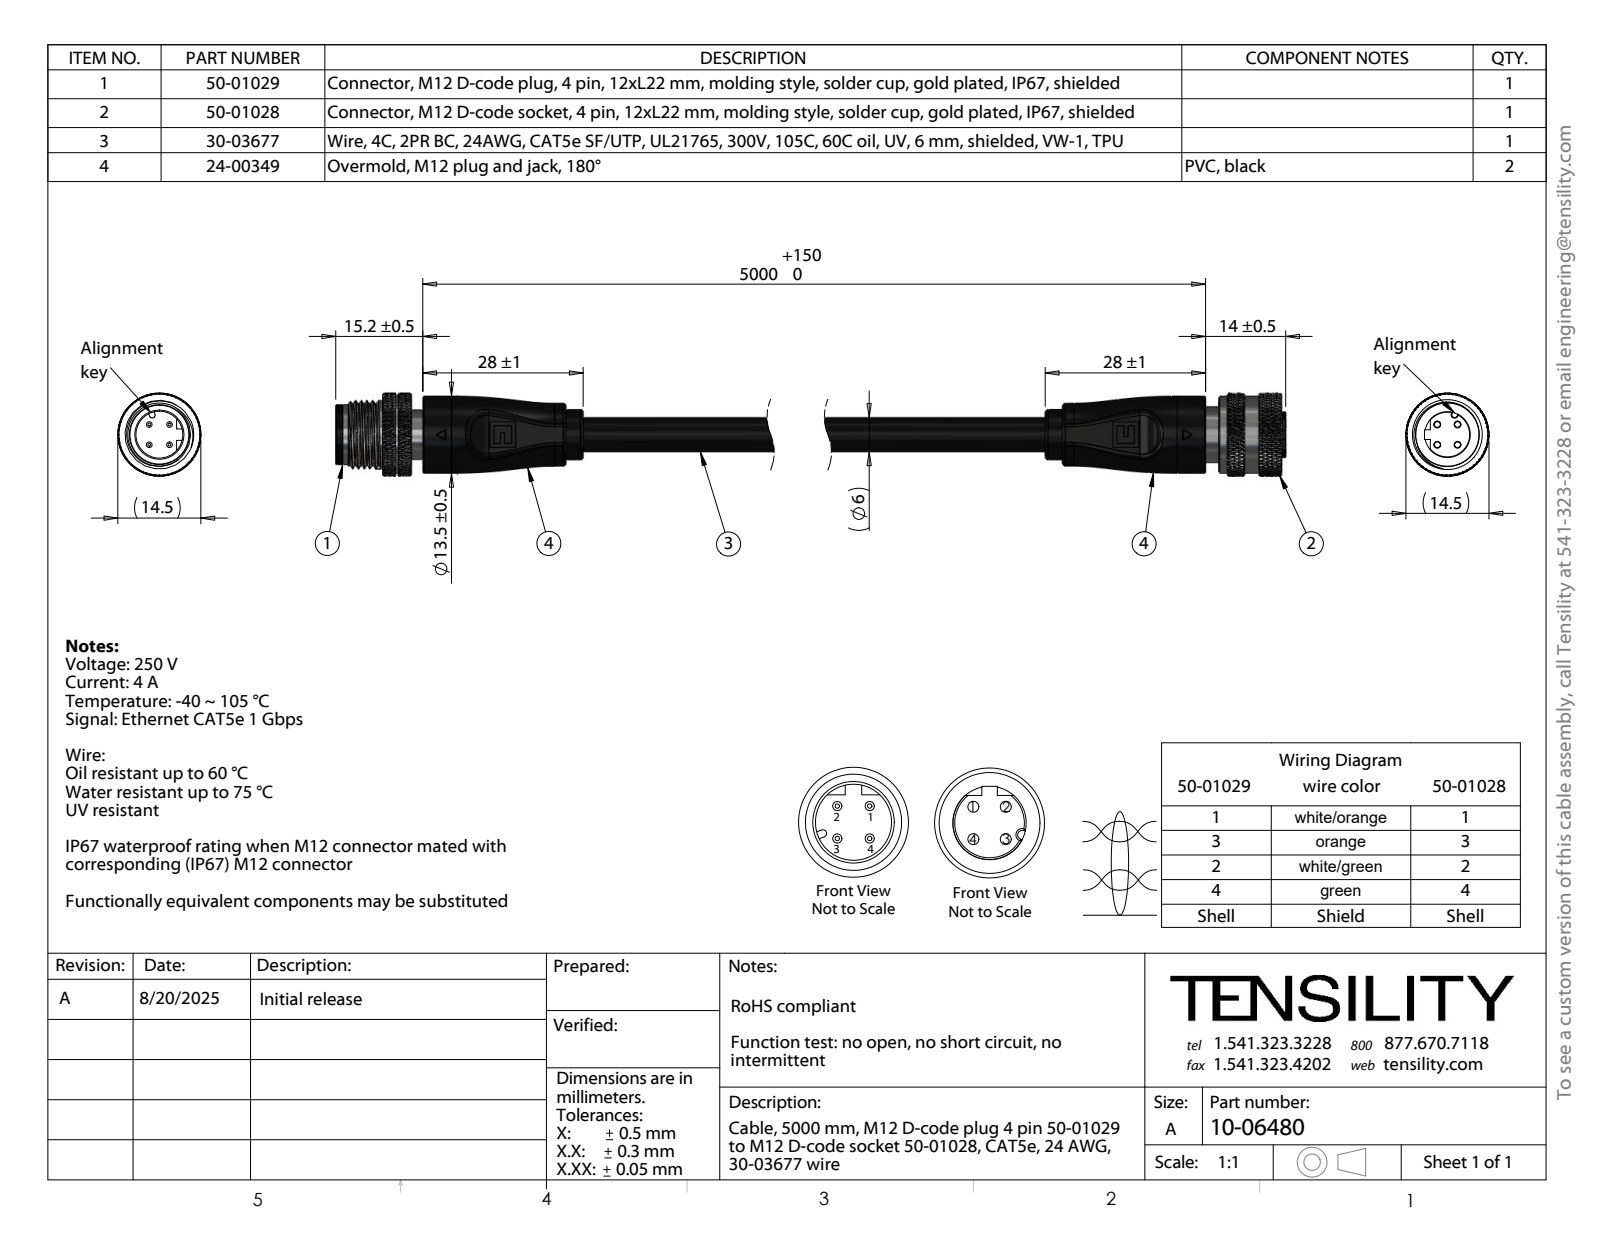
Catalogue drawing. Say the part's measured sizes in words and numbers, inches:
The part is named "24-00349_Mexico; 50-01028-03_默认; 50-01029-01_默认; 50-01029_默认 (+8 more)". Its 3-D file was written by "SolidWorks 2025 (CONFIG_CONTROL_DESIGN)". It is 53 solids with 5792 faces: 362 planar, 1477 cylindrical and 3953 other. Overall it measures 9.26 by 0.571 by 0.571 inches. Its volume is 0.838 cubic inches and its surface area 47.49 square inches. Round holes: 28 of diameter 0.008, 4 of diameter 0.039, 4 of diameter 0.041, 4 of diameter 0.043, 4 of diameter 0.047, 1 of diameter 0.124, 1 of diameter 0.126, 1 of diameter 0.14, 1 of diameter 0.323, 1 of diameter 0.374, 1 of diameter 0.394, 1 of diameter 0.441. Round bosses or shafts: 4 of diameter 0.063, 4 of diameter 0.059, 4 of diameter 0.055, 1 of diameter 0.571, 1 of diameter 0.547, 1 of diameter 0.531, 1 of diameter 0.472, 1 of diameter 0.433. Partial cylindrical surfaces (rounded edges, fillets, slot ends): 10 of radius 0.004, 6 of radius 0.016, 4 of radius 0.02, 2 of radius 0.059, 2 of radius 0.077, 2 of radius 0.197, 1 of radius 0.22, 1 of radius 0.266. The main face-to-face distances are 8.11, 0.276, 1.102, 7.008, 0.079, 8.189, 0.15, 8.339, 8.201, 0.228. The hole center spacings are 0.075, 0.014, 0.082, 0.042, 0.035, 0.043, 0.049, 0.071.
